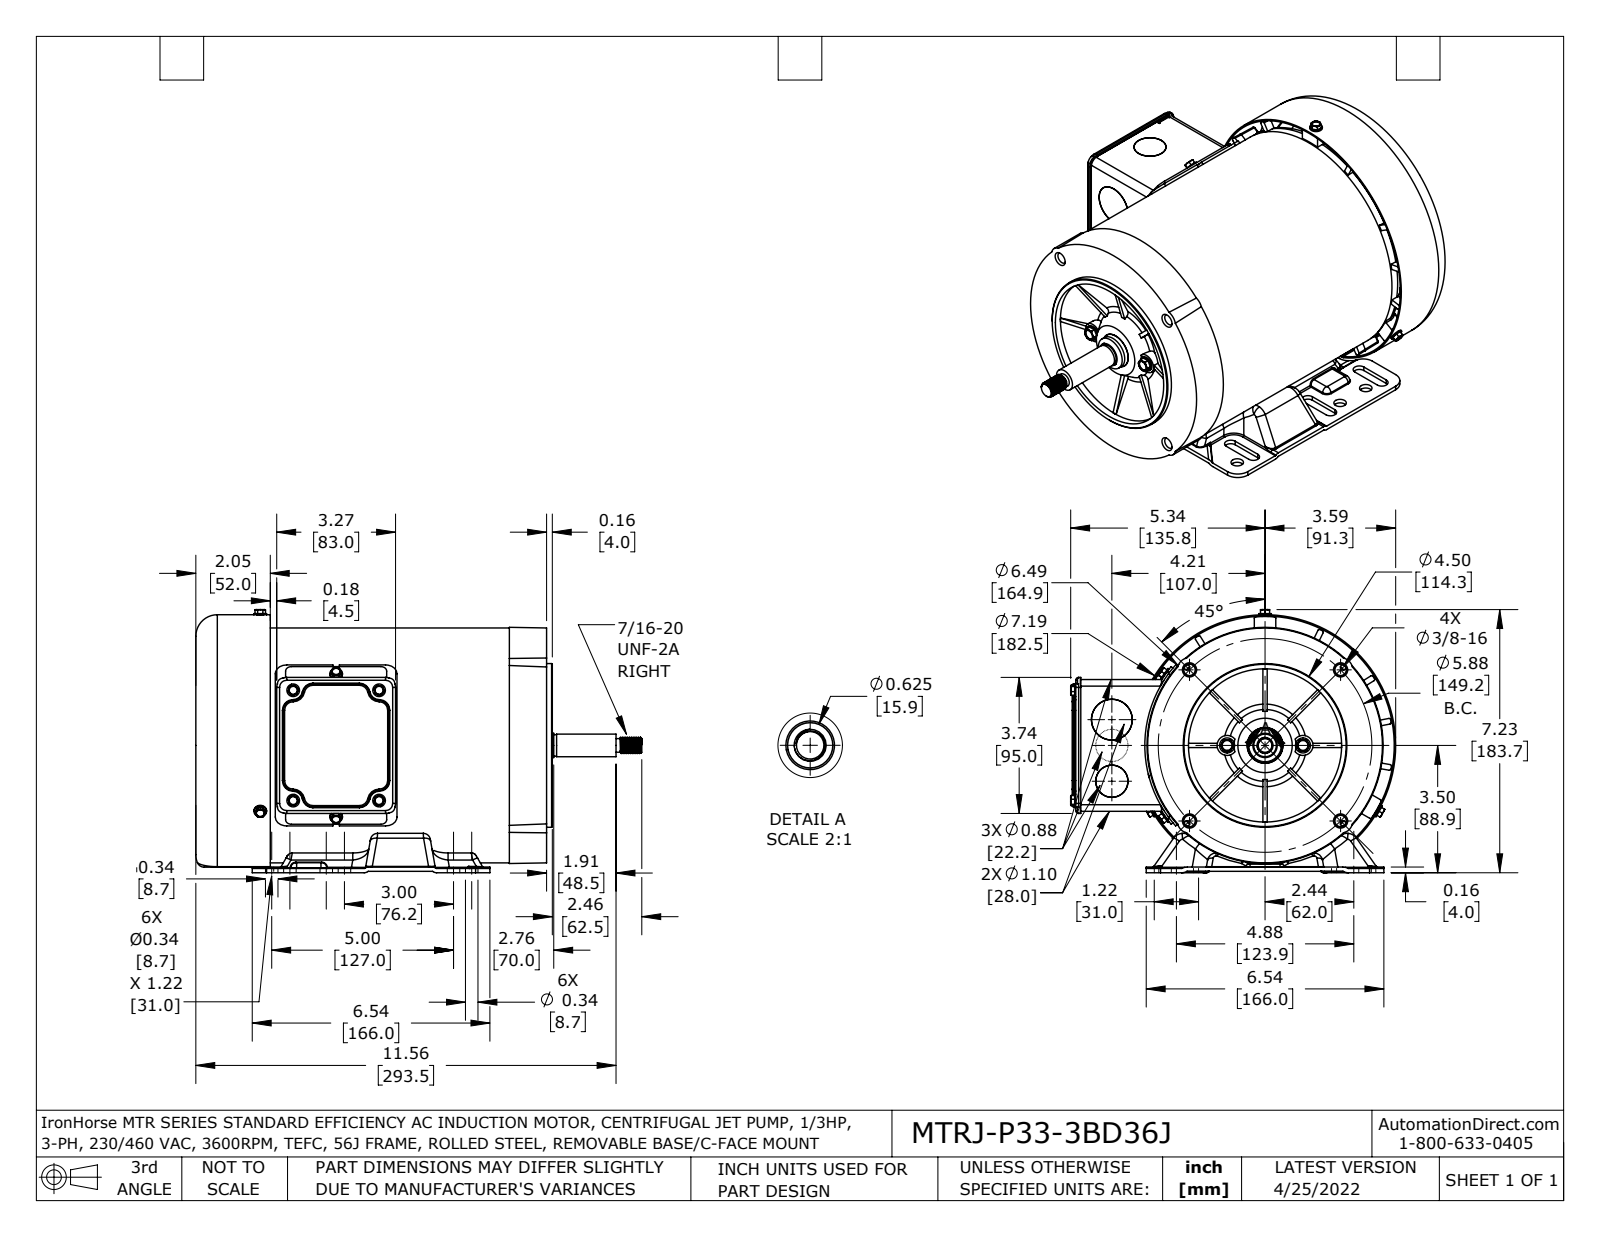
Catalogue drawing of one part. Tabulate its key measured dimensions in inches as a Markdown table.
| quantity | value |
| --- | --- |
| part name | MTRJ-P33-3BD36J redcmb1 coord fxt |
| STEP written by | SolidWorks 2021 (AUTOMOTIVE_DESIGN) |
| units | inches |
| bodies | 29 solids, 2729 faces (658 planar, 899 cylindrical, 1172 other) |
| overall size | 12.264 × 8.938 × 7.234 |
| volume | 46.25 in³ |
| surface area | 892.8 in² |
| round holes (diameter × count) | 0.197 × 10, 0.219 × 9, 0.276 × 8, 0.136 × 7, 0.217 × 6, 0.328 × 6, 0.344 × 6, 0.15 × 4, 0.177 × 4, 0.313 × 4, 0.134 × 2, 0.273 × 2 |
| round bosses / shafts (diameter × count) | 0.164 × 9, 0.348 × 8, 0.236 × 6, 0.414 × 2, 0.19 × 2, 7.185 × 1, 4.5 × 1, 0.945 × 1 |
| partial cylindrical surfaces (radius × count) | 0.118 × 109, 0.039 × 65, 0.157 × 32, 0.02 × 30, 0.138 × 26, 0.079 × 18, 0.276 × 18, 0.172 × 12 |
| main face-to-face distances | 0.039, 0.118, 0.063, 0.157, 9.646, 9.606, 0.079, 3.559, 3.087, 0.047 |
| hole center spacings | 4.221, 3.031, 0.094, 2.32, 2.409, 2.937, 2.979, 3.748 |
